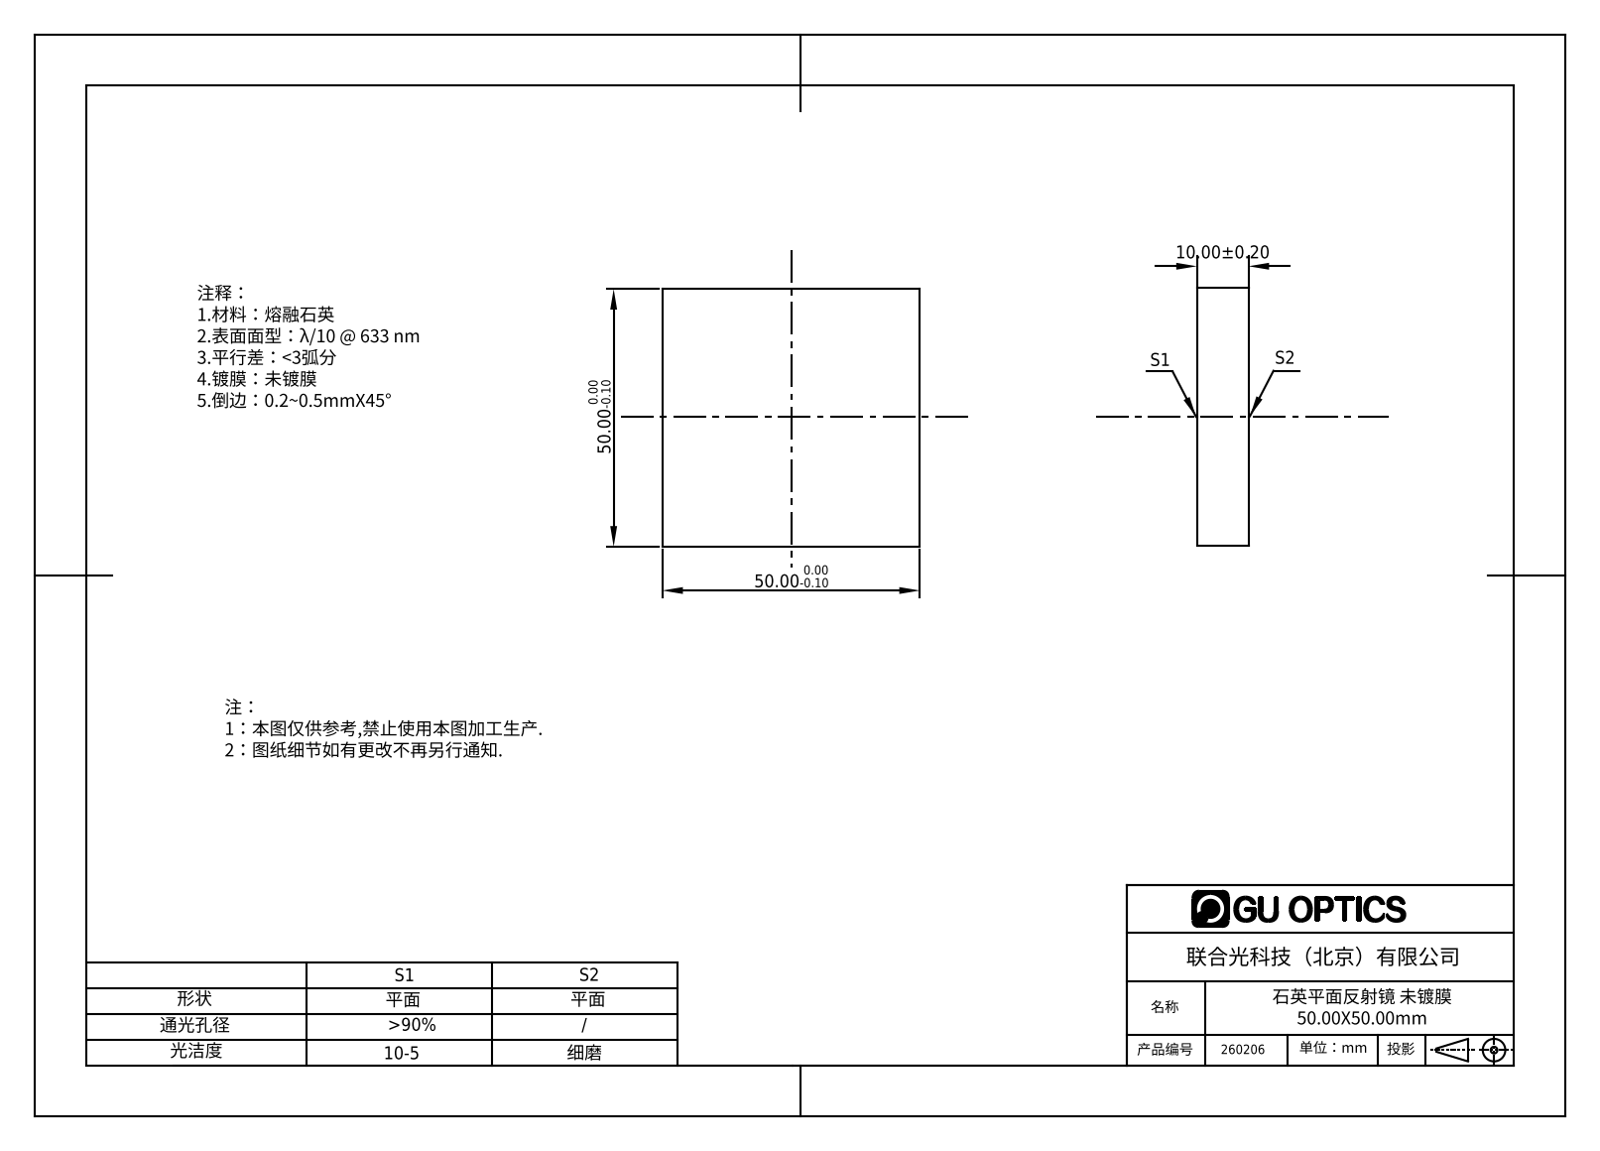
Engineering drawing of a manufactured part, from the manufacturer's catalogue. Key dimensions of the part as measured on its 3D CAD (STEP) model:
Part name (STEP PRODUCT): 260077
STEP written by: SolidWorks 2016 (AUTOMOTIVE_DESIGN)
Units: millimetres
Bodies: 1 solid, 6 faces (6 planar, 0 cylindrical, 0 other)
Overall size (bounding box): 50 × 50 × 10
Volume: 25 000 mm³ · Surface area: 7 000 mm²
Main face-to-face distances: 10, 50
